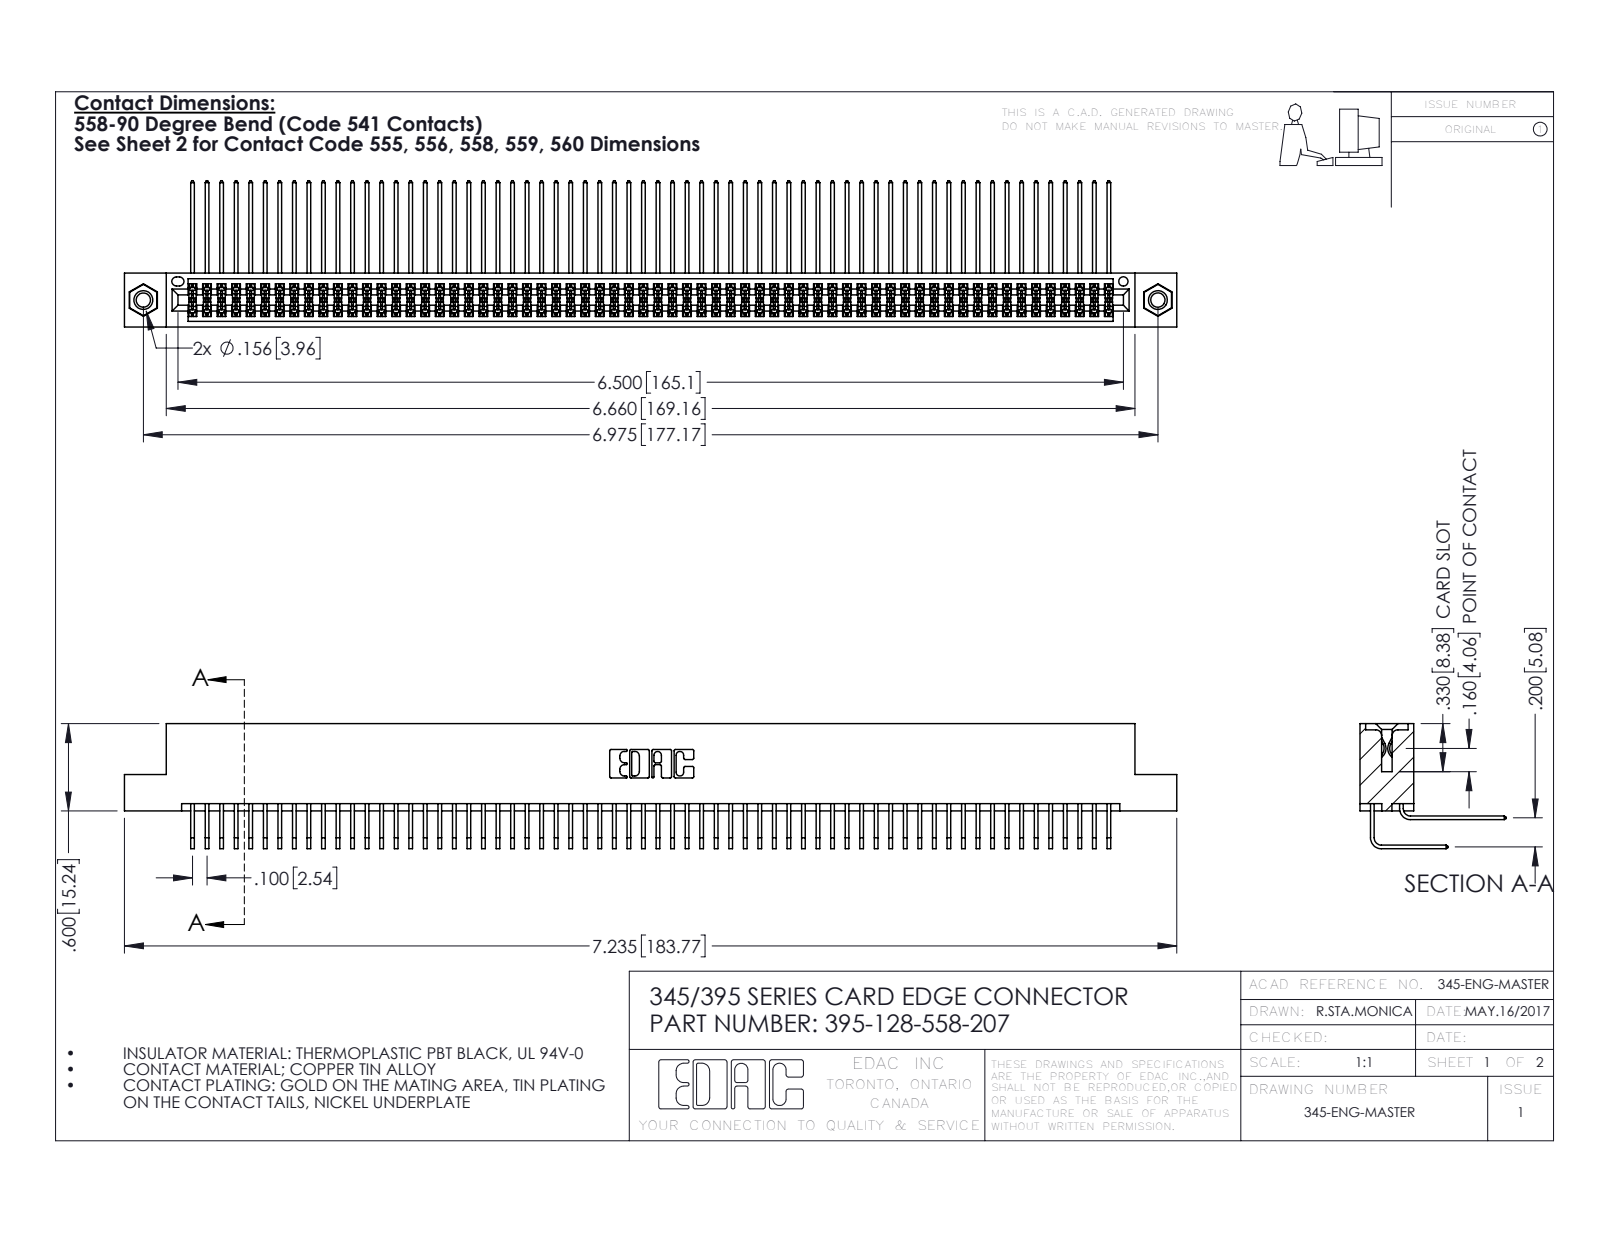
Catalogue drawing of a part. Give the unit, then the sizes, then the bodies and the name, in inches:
Units: inches
Overall size (bounding box): 7.235 × 1.005 × 0.859
Round holes (diameter × count): ⌀0.098 ×2, ⌀0.125 ×2, ⌀0.156 ×2, ⌀0.064 ×1
Round bosses / shafts (diameter × count): ⌀0.155 ×2
Partial cylindrical surfaces — rounded edges, fillets, slot ends (radius × count): R0.006 ×193, R0.01 ×22, R0.007 ×6, R0.031 ×6, R0.026 ×3, R0.014 ×2, R0.019 ×2, R0.022 ×2
Main face-to-face distances: 0.072, 0.298, 0.2, 0.37, 0.098, 0.272, 0.025, 0.225, 0.025, 0.175
Hole centre spacings: 0.27, 6.739, 6.975
Volume: 1.146 in³ · Surface area: 49.12 in²
Bodies: 131 solids, 6842 faces (4592 planar, 2234 cylindrical, 16 other)
Part name (STEP PRODUCT): 345-292-001_558 559 Tail - 1; 345 Part_Flush Mounting Lugs - 0.156 Dia-TI; 395-128-558-207; 345-250-001_345-250-005-103 (+1 more)
STEP written by: SolidWorks 2016 (CONFIG_CONTROL_DESIGN)
